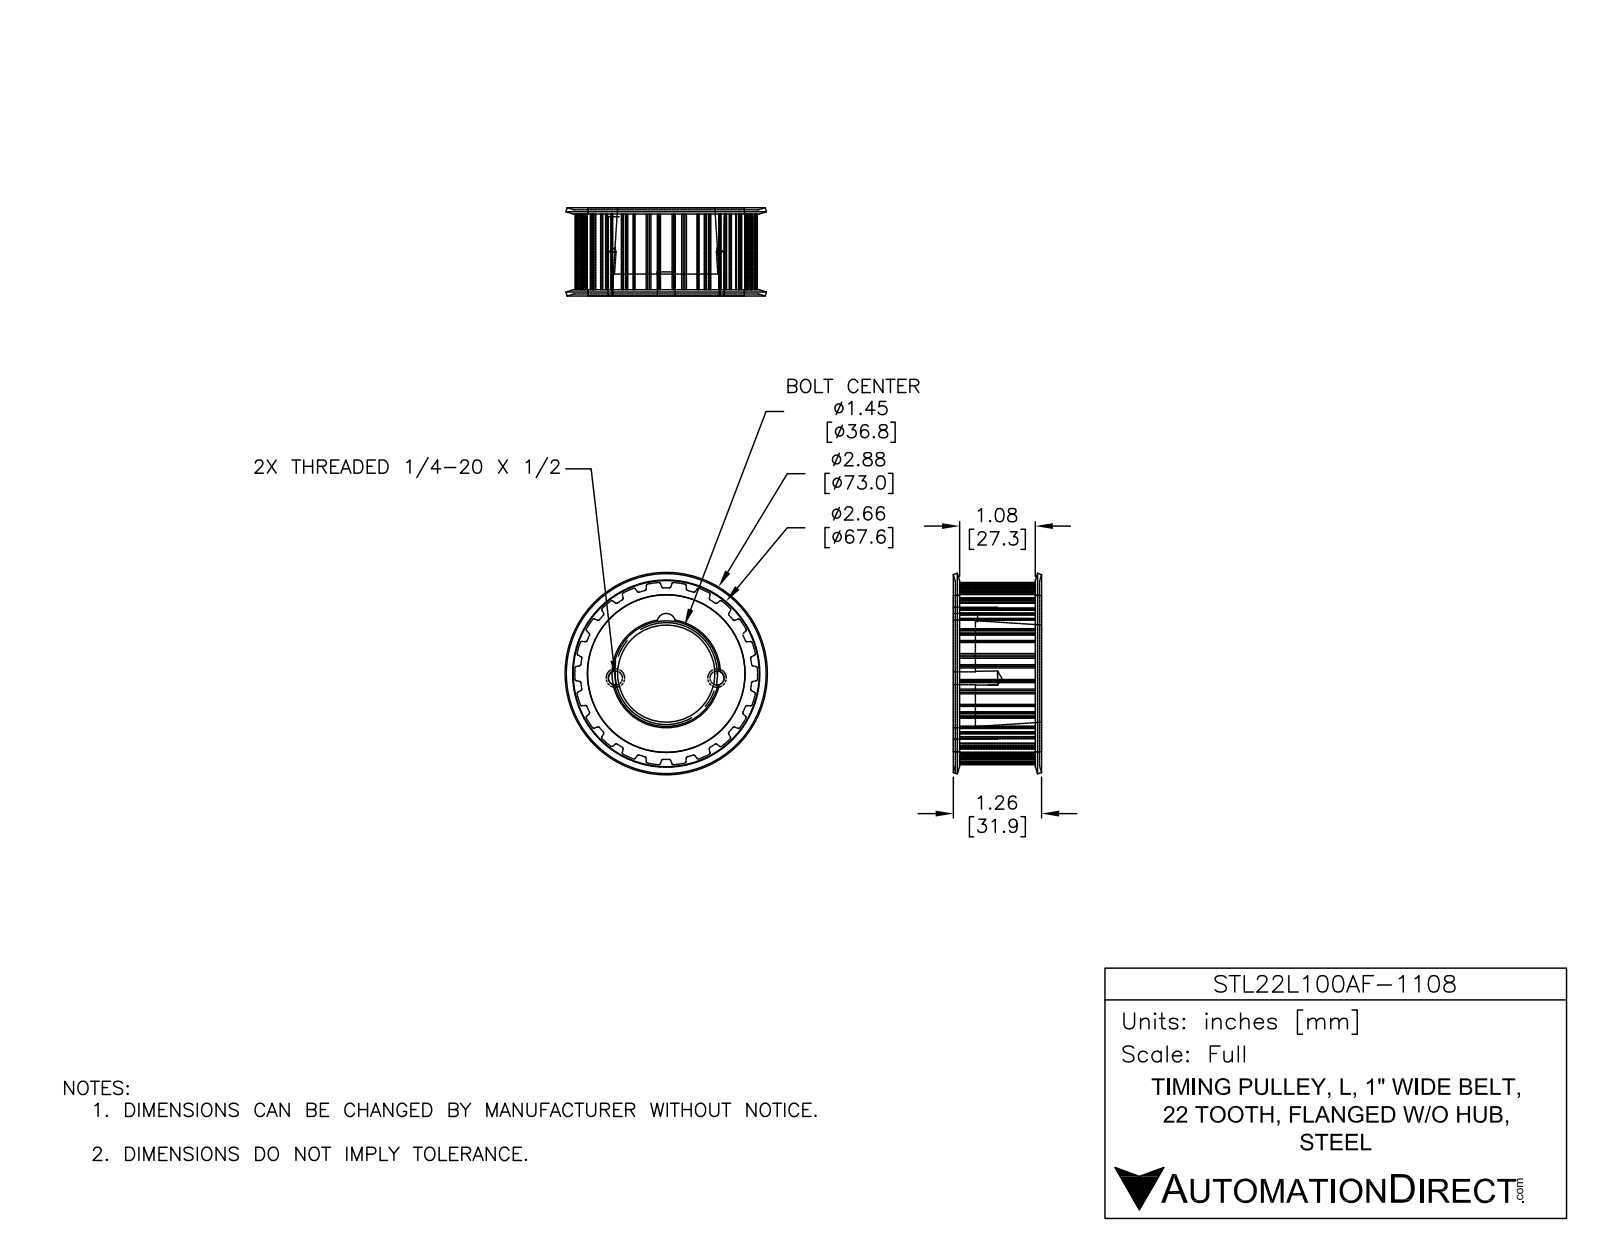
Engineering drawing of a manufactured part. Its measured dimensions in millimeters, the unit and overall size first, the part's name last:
Units: millimetres
Overall size (bounding box): 73.03 × 73.03 × 31.88
Round holes (diameter × count): ⌀39.12 ×1, ⌀56.92 ×1
Round bosses / shafts (diameter × count): ⌀56.83 ×1
Partial cylindrical surfaces — rounded edges, fillets, slot ends (radius × count): R0.25 ×44, R0.51 ×44, R2.54 ×2, R3.3 ×1, R32.97 ×1
Main face-to-face distances: 31.75, 0.7, 31.06, 30.36, 31.05, 0.69, 1.53, 28.83, 2.23, 29.52
Volume: 69 941 mm³ · Surface area: 21 003 mm²
Bodies: 1 solid, 237 faces (78 planar, 142 cylindrical, 17 other)
Part name (STEP PRODUCT): STL22L100AF-1108
STEP written by: SolidWorks 2018 (AUTOMOTIVE_DESIGN)
